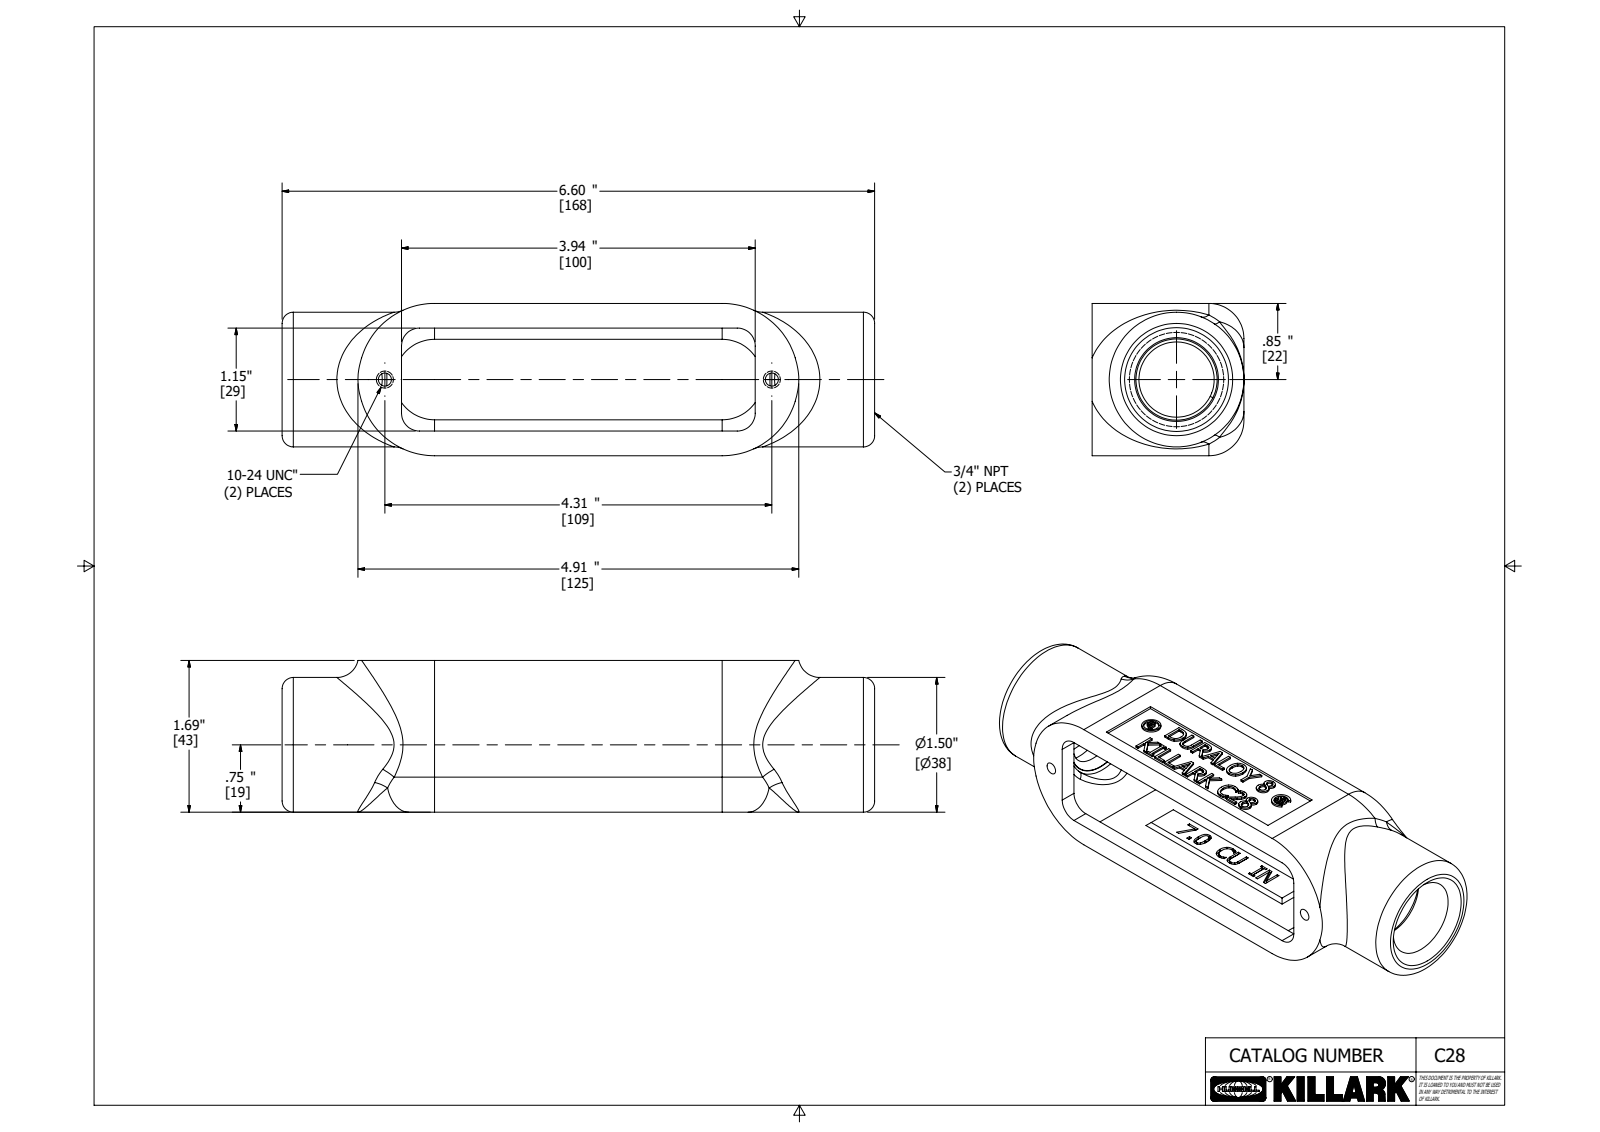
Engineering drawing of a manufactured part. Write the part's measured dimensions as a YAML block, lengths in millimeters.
part_name: "21707-2"
step_written_by: "Autodesk Inventor 2018 (AUTOMOTIVE_DESIGN)"
units: millimeters
bodies: {solids: 1, faces: 493, planar: 270, cylindrical: 36, other: 187}
overall_size: [167.6, 43.1, 42.9]
volume: 105700
surface_area: 41540
round_holes:
  - {diameter: 3.7, count: 2}
  - {diameter: 4.7, count: 1}
  - {diameter: 26.8, count: 1}
round_bosses_or_shafts:
  - {diameter: 38.1, count: 1}
  - {diameter: 5.8, count: 1}
partial_cylinders:
  - {radius: 5.1, count: 6}
  - {radius: 9.9, count: 2}
  - {radius: 16.5, count: 2}
  - {radius: 21.5, count: 2}
  - {radius: 0.2, count: 1}
  - {radius: 0.7, count: 1}
  - {radius: 1.3, count: 1}
  - {radius: 1.9, count: 1}
face_to_face_distances: [38, 5.1, 4.9, 42.9, 38.1, 32.9, 43.1, 0.8, 42.3, 37.2]
hole_center_spacings: [109.5]
